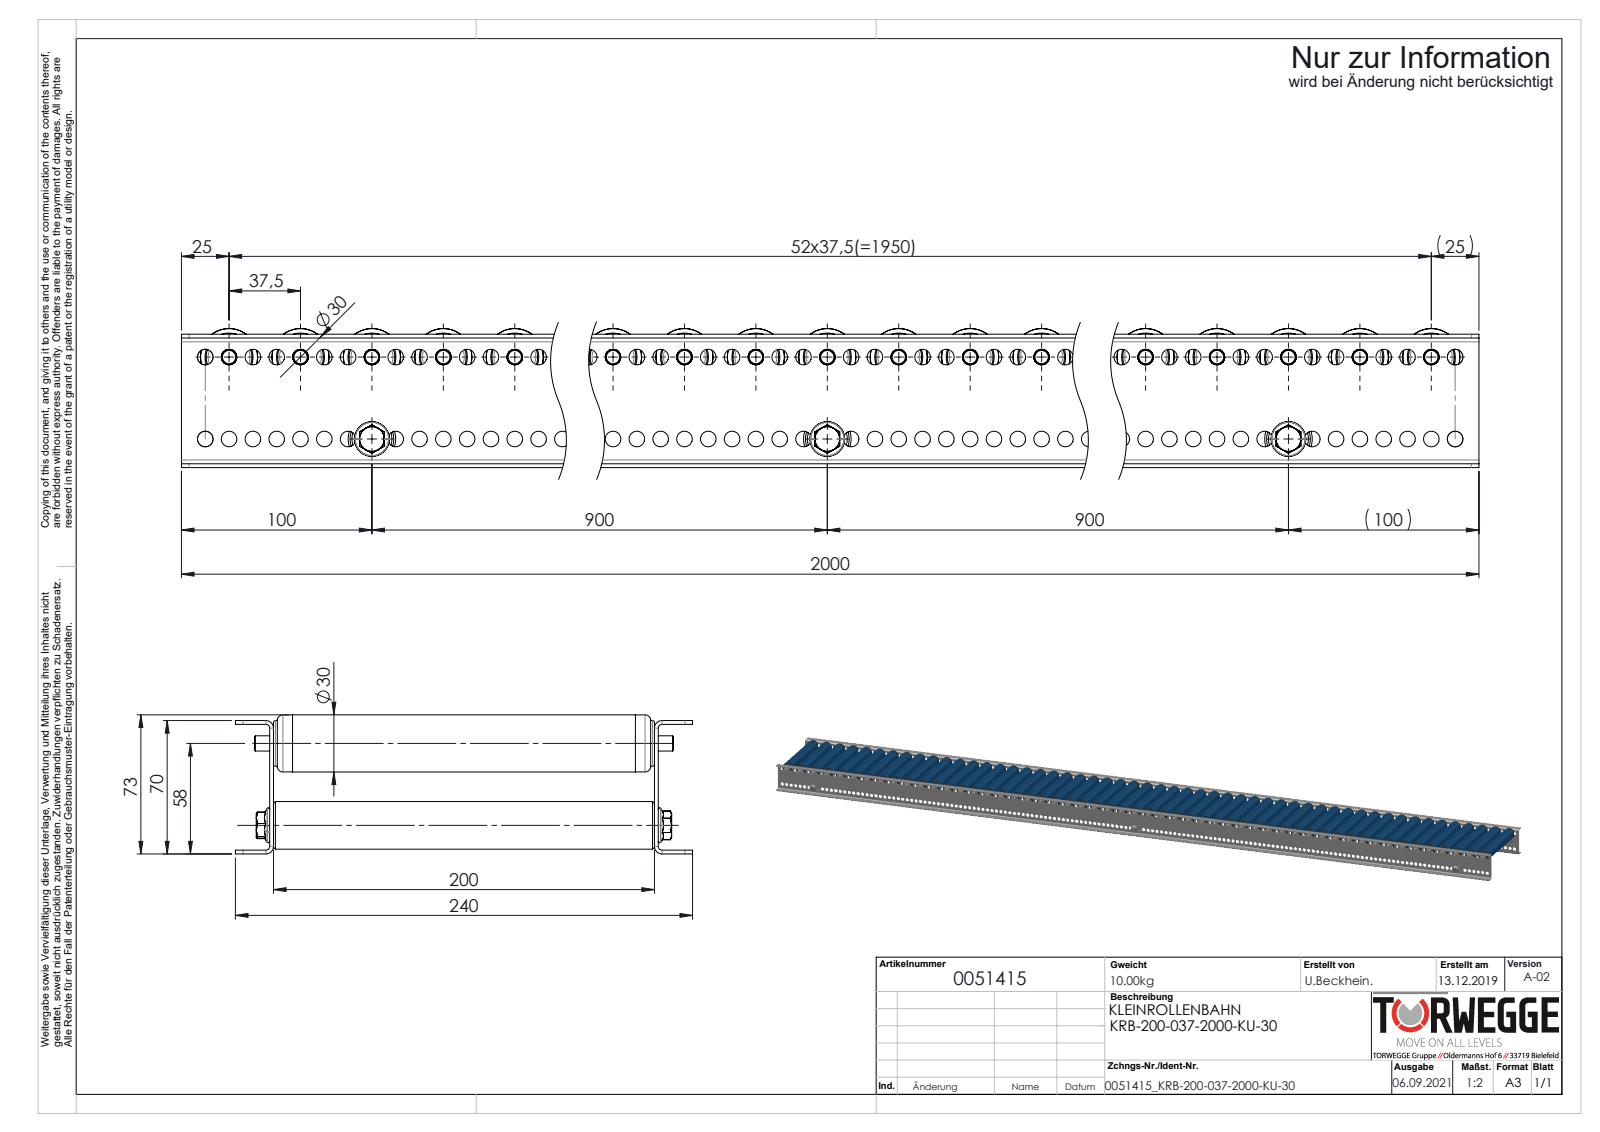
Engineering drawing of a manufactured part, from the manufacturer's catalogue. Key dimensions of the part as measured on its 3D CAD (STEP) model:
Part name (STEP PRODUCT): Profil_KRB-20x70x20x2_KFG_S100232_U-PROFIL-20-70-20-2-KRB-30-L=2000; 0051415; KUT50-30x1,8-KB-A8-FA_KFG_0034504TWG_KUT50-30x1,8-KB-A8-FA-EL=200; S100995_TYP-KUT50-30x1,8-A8 (+4 more)
STEP written by: SolidWorks 2020 (AUTOMOTIVE_DESIGN)
Units: millimetres
Bodies: 123 solids, 12584 faces (3872 planar, 4740 cylindrical, 3972 other)
Overall size (bounding box): 2000 × 240 × 73
Volume: 2 996 000 mm³ · Surface area: 3 538 000 mm²
Round holes (diameter × count): ⌀8.2 ×318, ⌀8.1 ×53, ⌀22.6 ×53, ⌀25.2 ×53, ⌀6.8 ×3, ⌀21 ×3
Round bosses / shafts (diameter × count): ⌀8 ×56, ⌀30 ×53, ⌀29.9 ×53, ⌀26.5 ×53, ⌀26.4 ×53, ⌀24 ×53, ⌀25 ×3
Partial cylindrical surfaces — rounded edges, fillets, slot ends (radius × count): R5.05 ×53, R4 ×8, R2 ×4
Main face-to-face distances: 2, 202, 200, 68, 204, 70, 66, 10, 190, 12
Hole centre spacings: 12.5, 25, 37.5, 50, 62.5, 75, 87.5, 100
